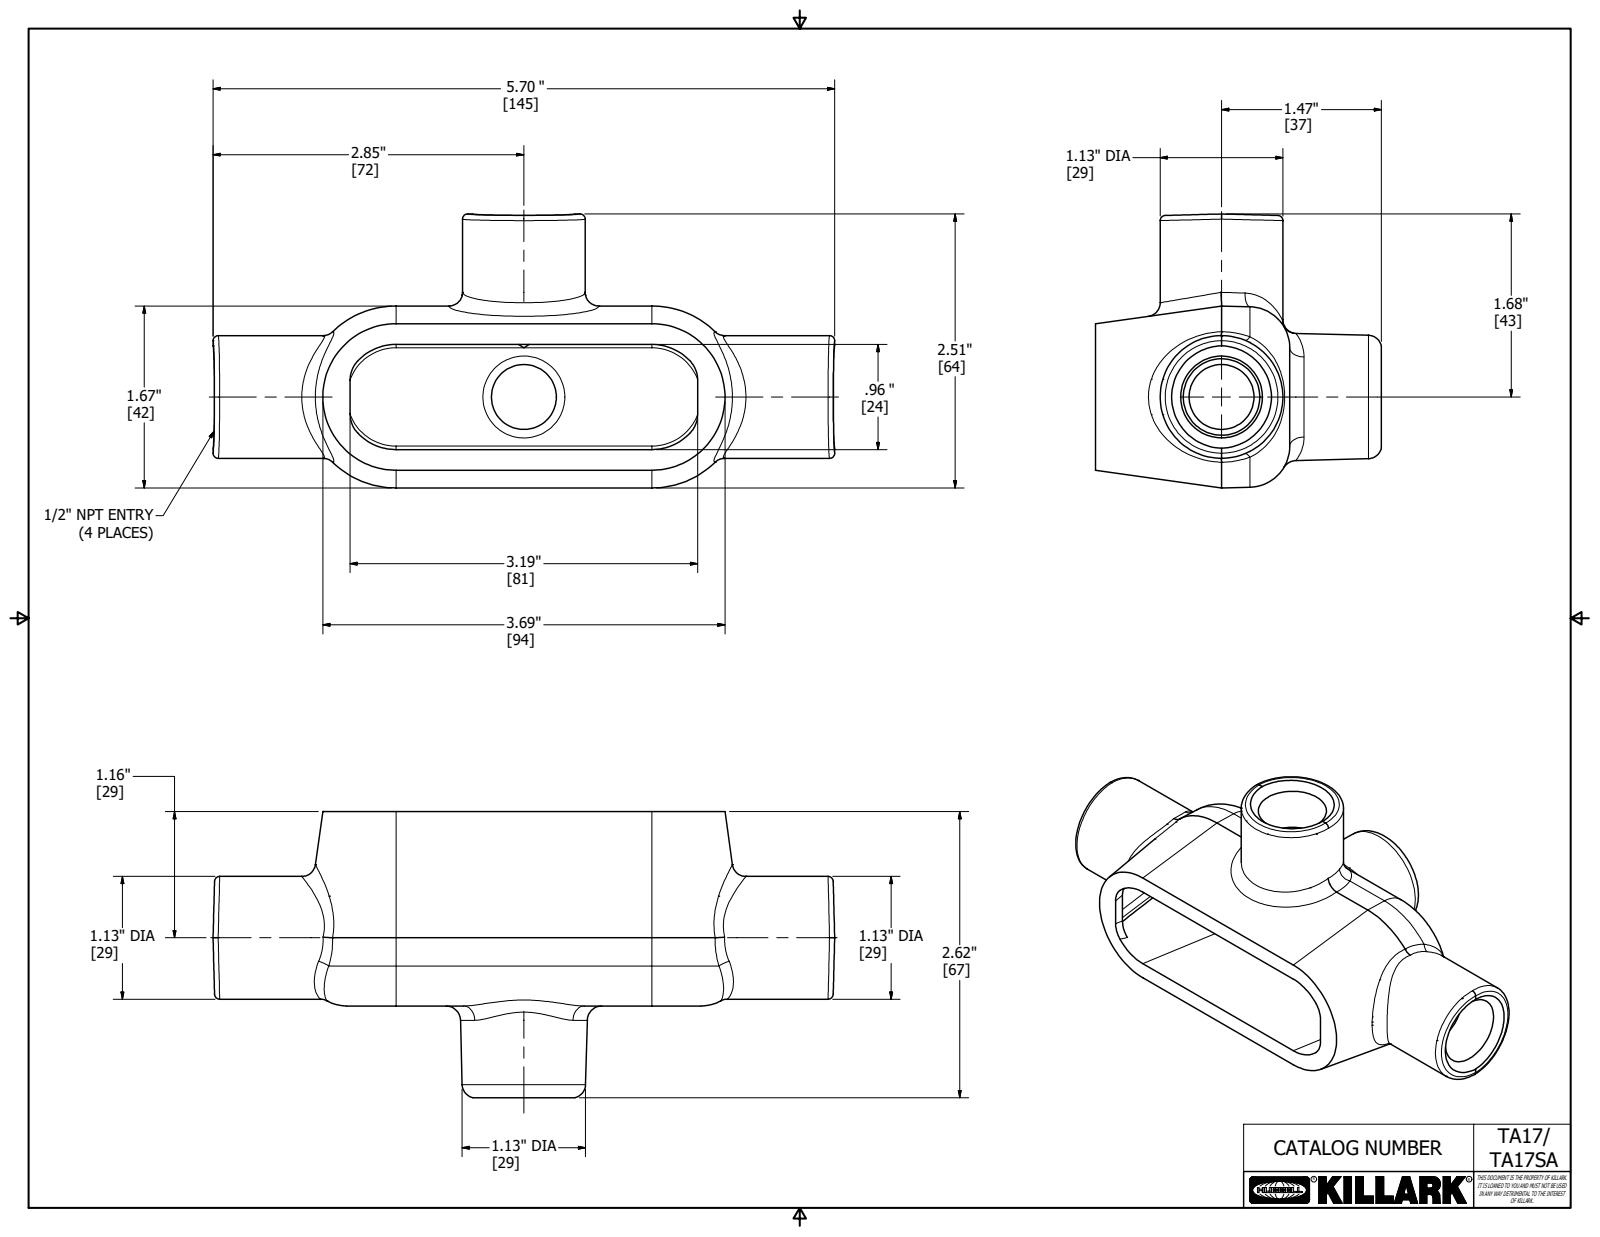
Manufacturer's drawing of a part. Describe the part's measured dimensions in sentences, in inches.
The part is named "17646". Its 3-D file was written by "Autodesk Inventor 2018 (AUTOMOTIVE_DESIGN)". It is 1 solid with 152 faces: 47 planar, 29 cylindrical and 76 other. Overall it measures 5.7 by 2.623 by 2.512 inches. Its volume is 5.216 cubic inches and its surface area 60.21 square inches. Round holes: 3 of diameter 0.844, 1 of diameter 0.875. Round bosses or shafts: 2 of diameter 1.125. Partial cylindrical surfaces (rounded edges, fillets, slot ends): 8 of radius 0.06, 4 of radius 0.05, 2 of radius 0.187, 2 of radius 0.375, 1 of radius 0.437. The main face-to-face distances are 0.187, 1.594, 0.188, 1.782, 0.189, 0.156, 0.031, 1.751, 5.7, 1.673.
